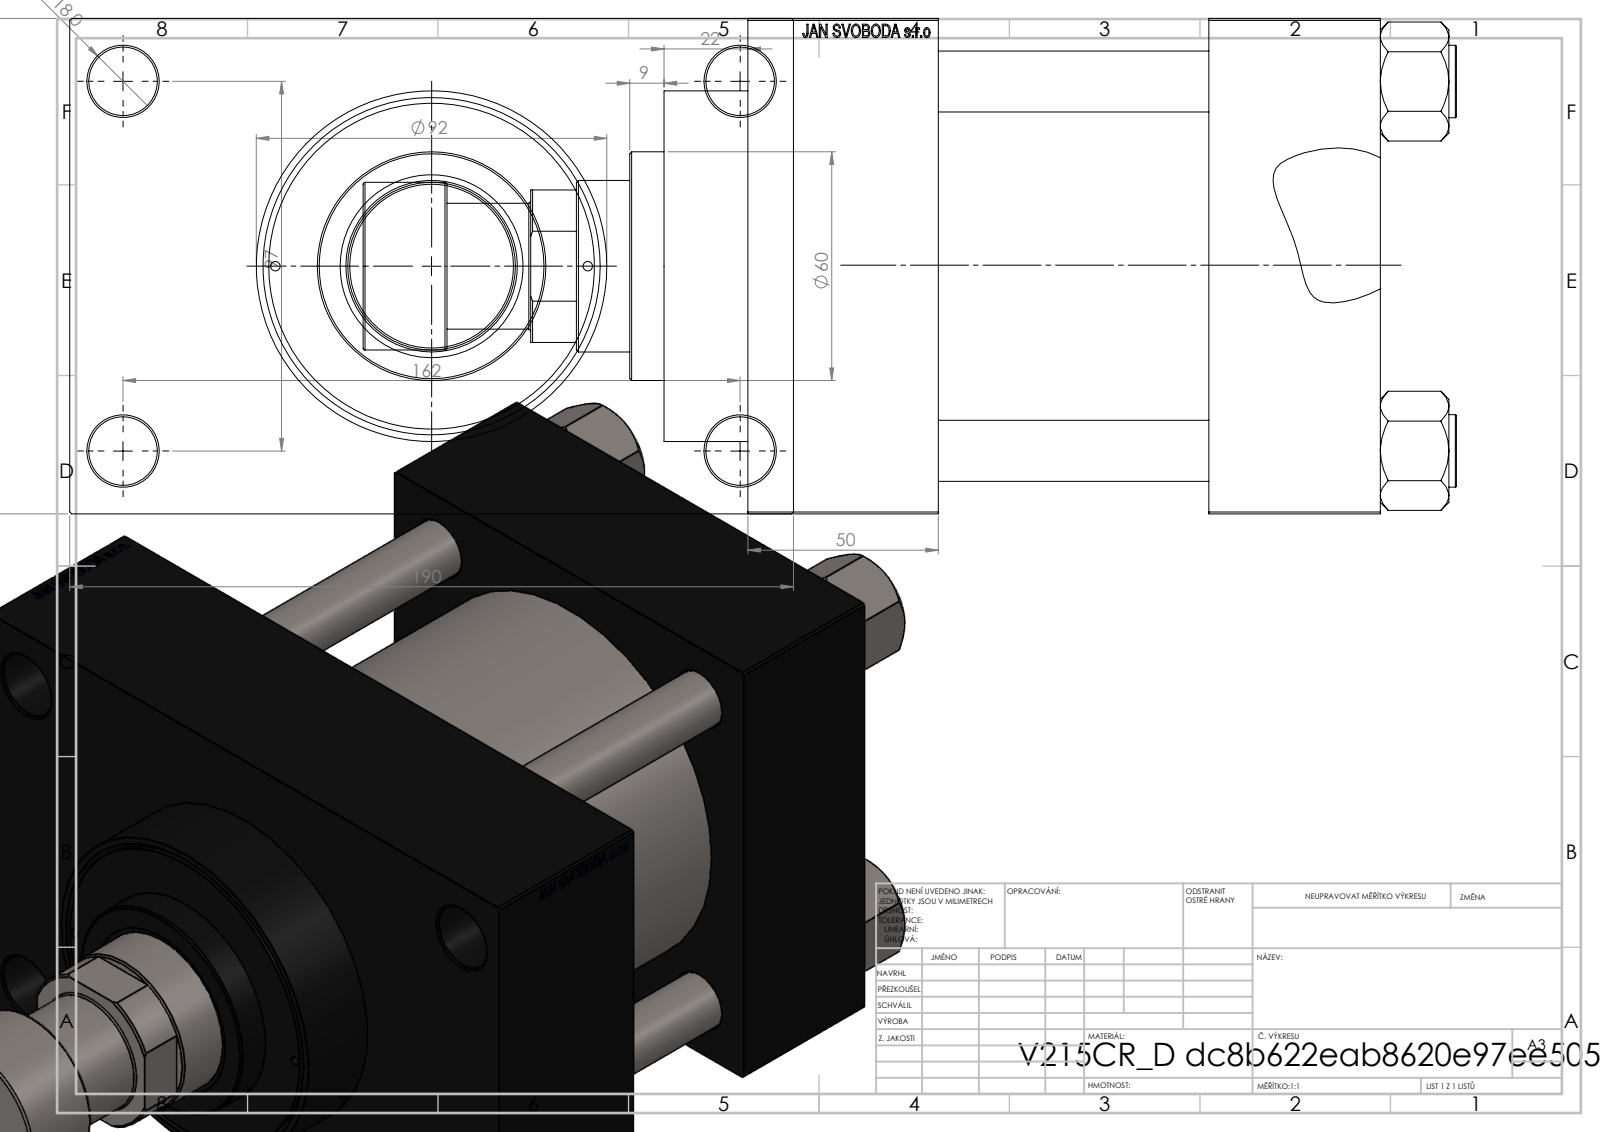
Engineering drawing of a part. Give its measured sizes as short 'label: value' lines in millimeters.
name: V215CR_VCP_D; V215_VC_A; V215CR_ROD_END_F; V215CR_D_Body (+2 more)
written by: SolidWorks 2019 (CONFIG_CONTROL_DESIGN)
unit: mm
bodies: 12 solids, 1172 faces (550 planar, 96 cylindrical, 526 other)
size: 287 × 190 × 130
volume: 2 642 000 mm³; area: 363 101 mm²
holes: 4× ⌀16, 4× ⌀18, 2× ⌀2.5, 2× ⌀7, 2× ⌀26.44, 2× ⌀35, 1× ⌀31.5, 1× ⌀45, 1× ⌀48, 1× ⌀76, 1× ⌀85.5, 1× ⌀100
bosses: 4× ⌀19, 1× ⌀106, 1× ⌀92, 1× ⌀60, 1× ⌀44, 1× ⌀33
face distances: 130, 116, 45, 71, 166, 121, 50, 30, 160, 70
hole spacings: 32.55, 49.02, 62.87, 68.52, 94.41, 96.9, 101.73, 102.27
